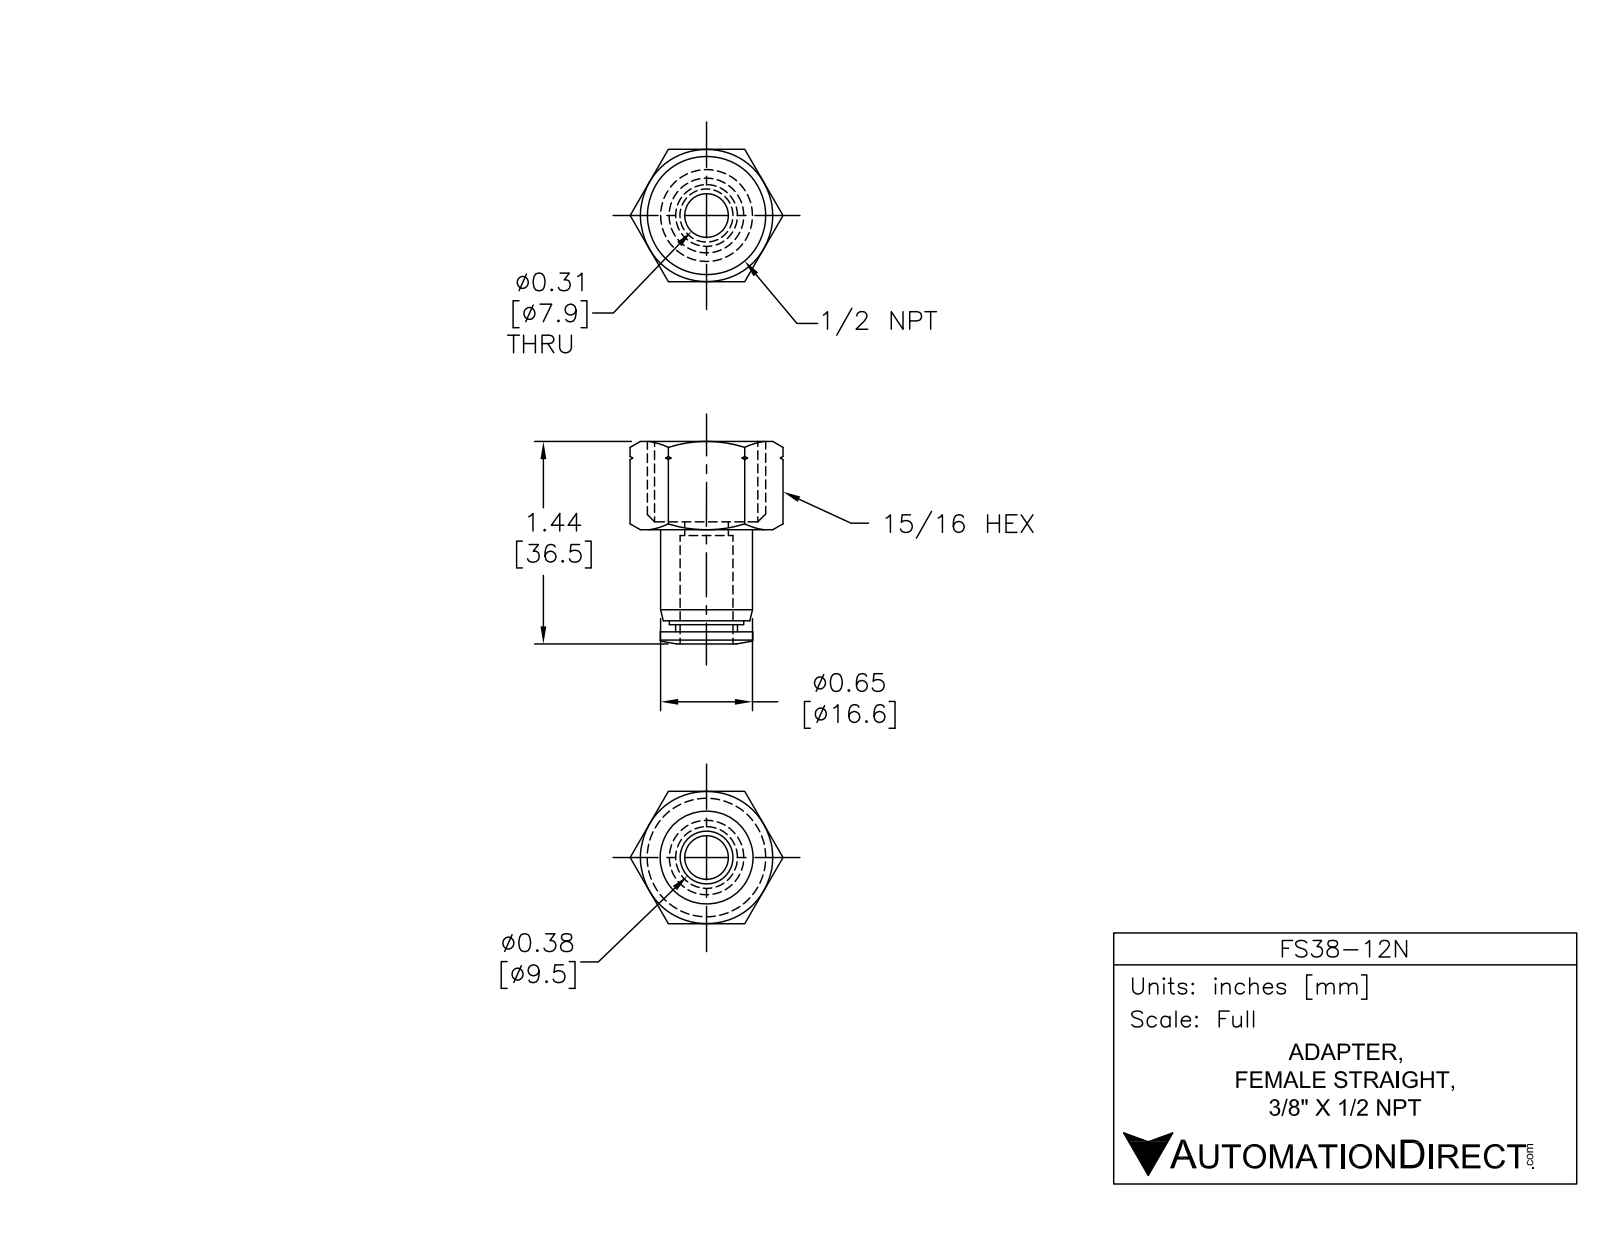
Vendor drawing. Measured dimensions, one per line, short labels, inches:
name: FS38-12N
written by: SolidWorks 2015 (AUTOMOTIVE_DESIGN)
unit: in
bodies: 1 solid, 61 faces (13 planar, 12 cylindrical, 36 other)
size: 1.445 × 1.091 × 0.945
volume: 0.343 in³; area: 7.772 in²
holes: 1× ⌀0.315, 1× ⌀0.386
bosses: 1× ⌀0.661, 1× ⌀0.656, 1× ⌀0.531, 1× ⌀0.441
face distances: 0.945, 0.059, 0.787, 0.728, 0.571, 0.63, 1.358, 1.28, 0.709, 0.65
